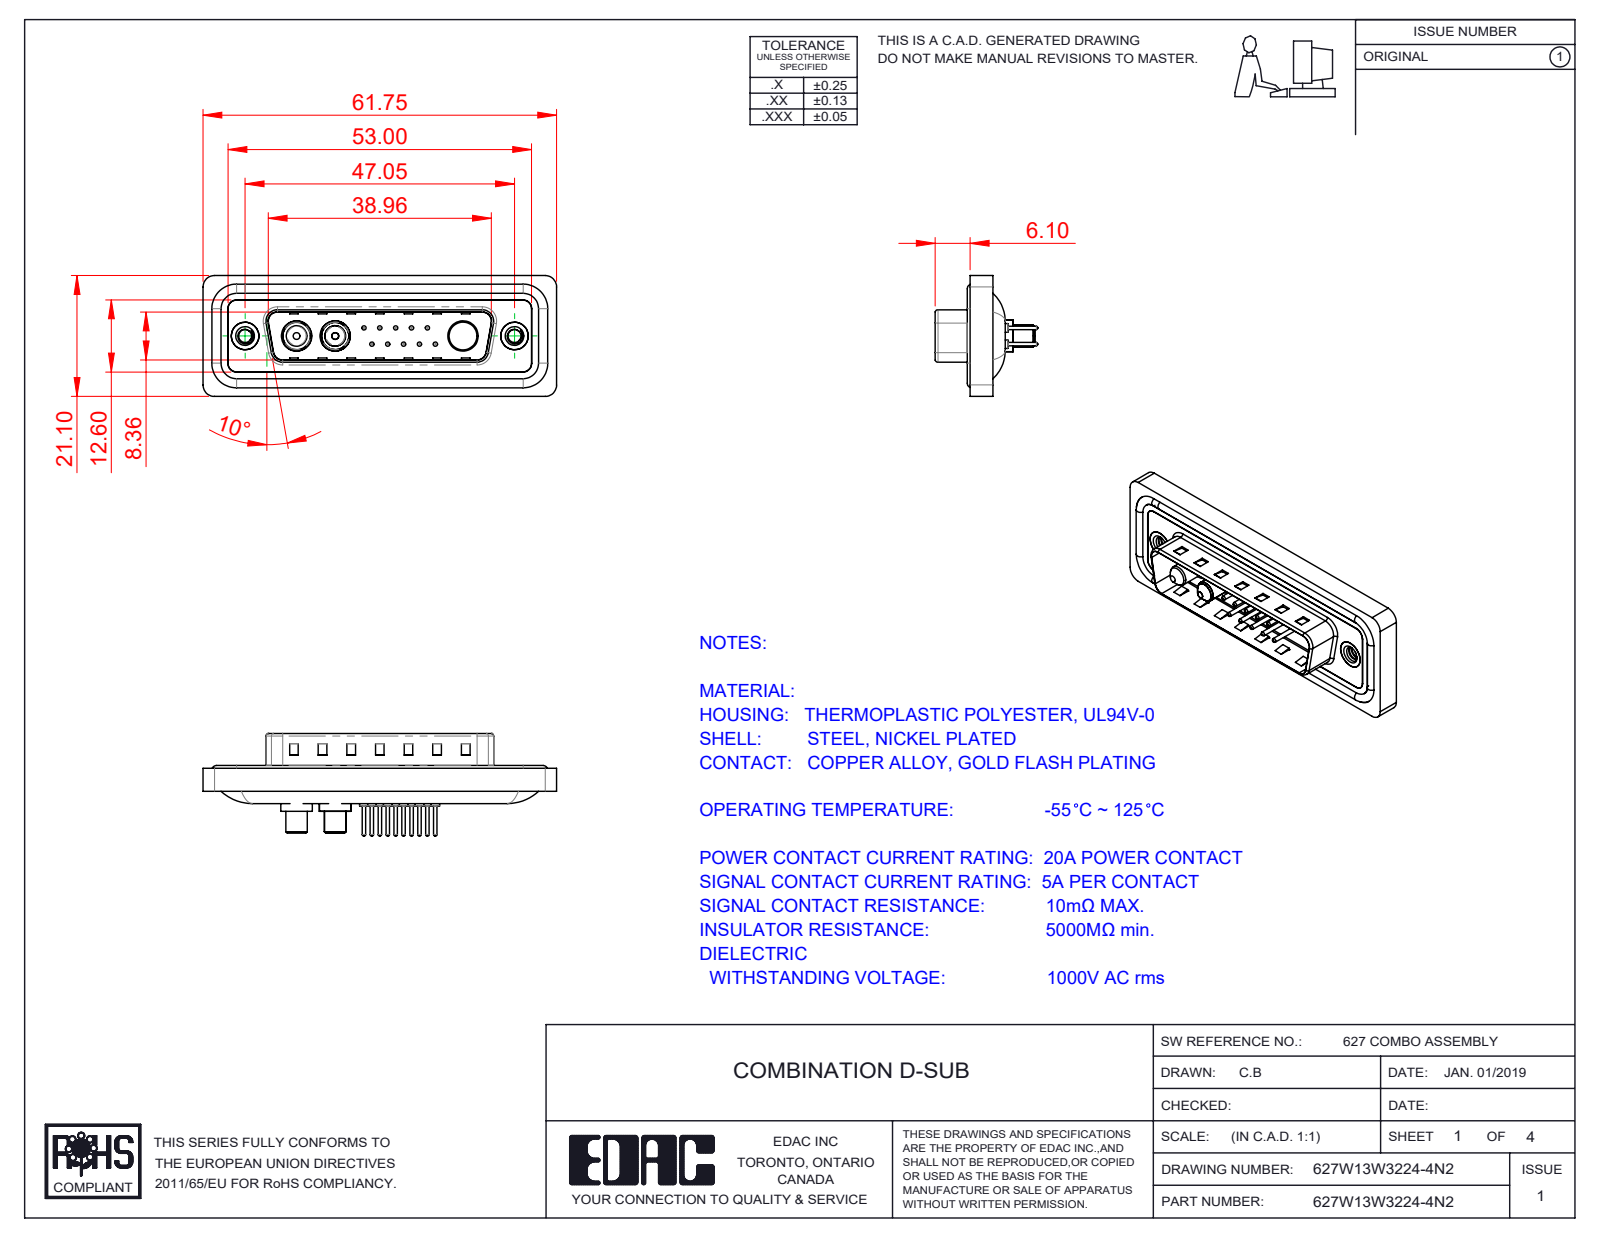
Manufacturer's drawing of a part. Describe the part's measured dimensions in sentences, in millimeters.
The part is named "627Combo Shell Rear_25 Contacts; 627Combo Shell Front_25 Contacts; 627Combo Housing_13W3; 627Combo Contact Row 2_24 (+5 more)". Its 3-D file was written by "SolidWorks 2020 (CONFIG_CONTROL_DESIGN)". It is 23 solids with 970 faces: 309 planar, 385 cylindrical and 276 other. Overall it measures 61.75 by 21.1 by 17.9 millimeters. Its volume is 7 391 cubic millimeters and its surface area 11 907 square millimeters. Round holes: 10 of diameter 0.75, 10 of diameter 1.6, 10 of diameter 2, 3 of diameter 4.85, 3 of diameter 5.3, 2 of diameter 2.26, 2 of diameter 4, 2 of diameter 4.8, 2 of diameter 5. Round bosses or shafts: 10 of diameter 1.5, 10 of diameter 0.6, 4 of diameter 1.6, 2 of diameter 5.5, 2 of diameter 5.2, 2 of diameter 4.9, 2 of diameter 4.75, 2 of diameter 3.75. Partial cylindrical surfaces (rounded edges, fillets, slot ends): 22 of radius 1.5, 18 of radius 2, 8 of radius 0.5, 8 of radius 1.6, 4 of radius 0.25, 4 of radius 0.6, 4 of radius 0.65, 4 of radius 0.9. The main face-to-face distances are 0.4, 1.5, 1.1, 1.6, 0.5, 3.1, 2.9, 0.82, 9.58, 4.1. The hole center spacings are 3.16, 2.77, 5.04, 5.54, 7.49, 5.03, 8.31, 10.11.
